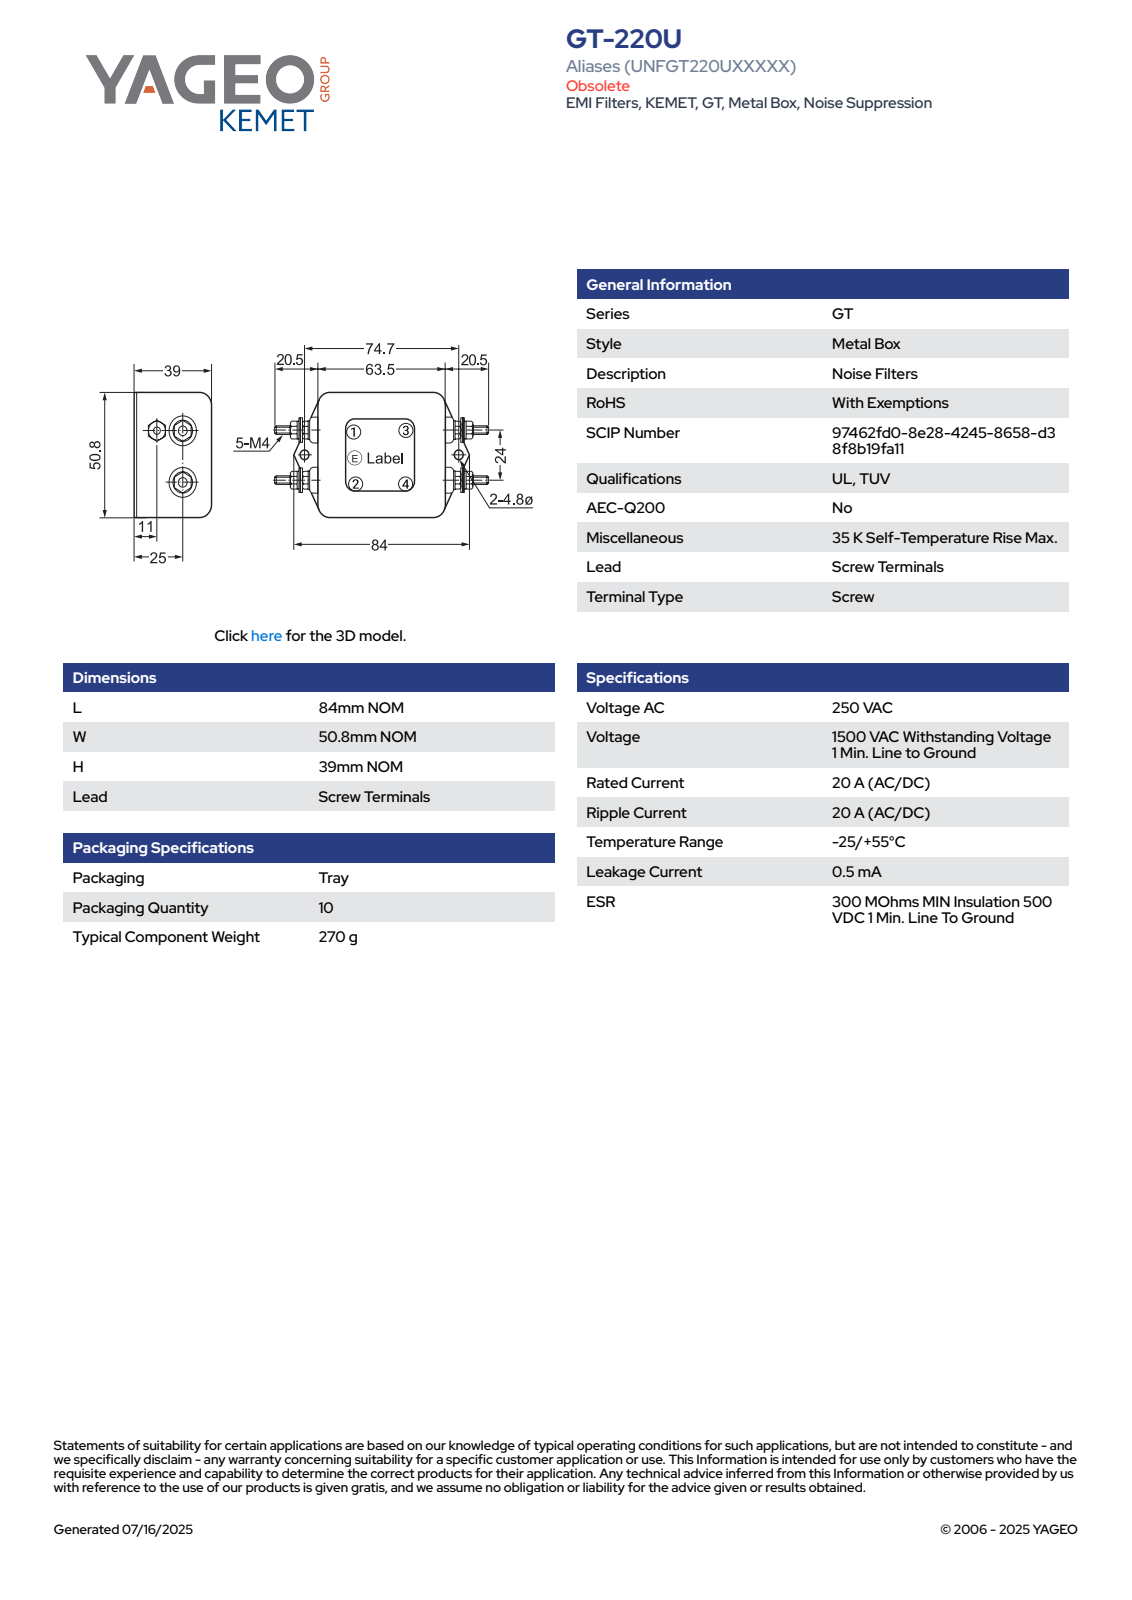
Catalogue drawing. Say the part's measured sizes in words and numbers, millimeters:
The part is named "Default". Its 3-D file was written by "SolidWorks 2014 (AUTOMOTIVE_DESIGN)". It is 1 solid with 172 faces: 90 planar, 60 cylindrical and 22 other. Overall it measures 104.5 by 50.8 by 39.01 millimeters. Its volume is 128 323 cubic millimeters and its surface area 17 741 square millimeters. Round holes: 2 of diameter 4.8. Round bosses or shafts: 3 of diameter 8, 3 of diameter 6, 3 of diameter 4. Partial cylindrical surfaces (rounded edges, fillets, slot ends): 8 of radius 3. The main face-to-face distances are 39, 50.8, 63.5, 1, 38, 81.5, 9.5, 73, 8.5, 72. The hole center spacings are 74.7.
